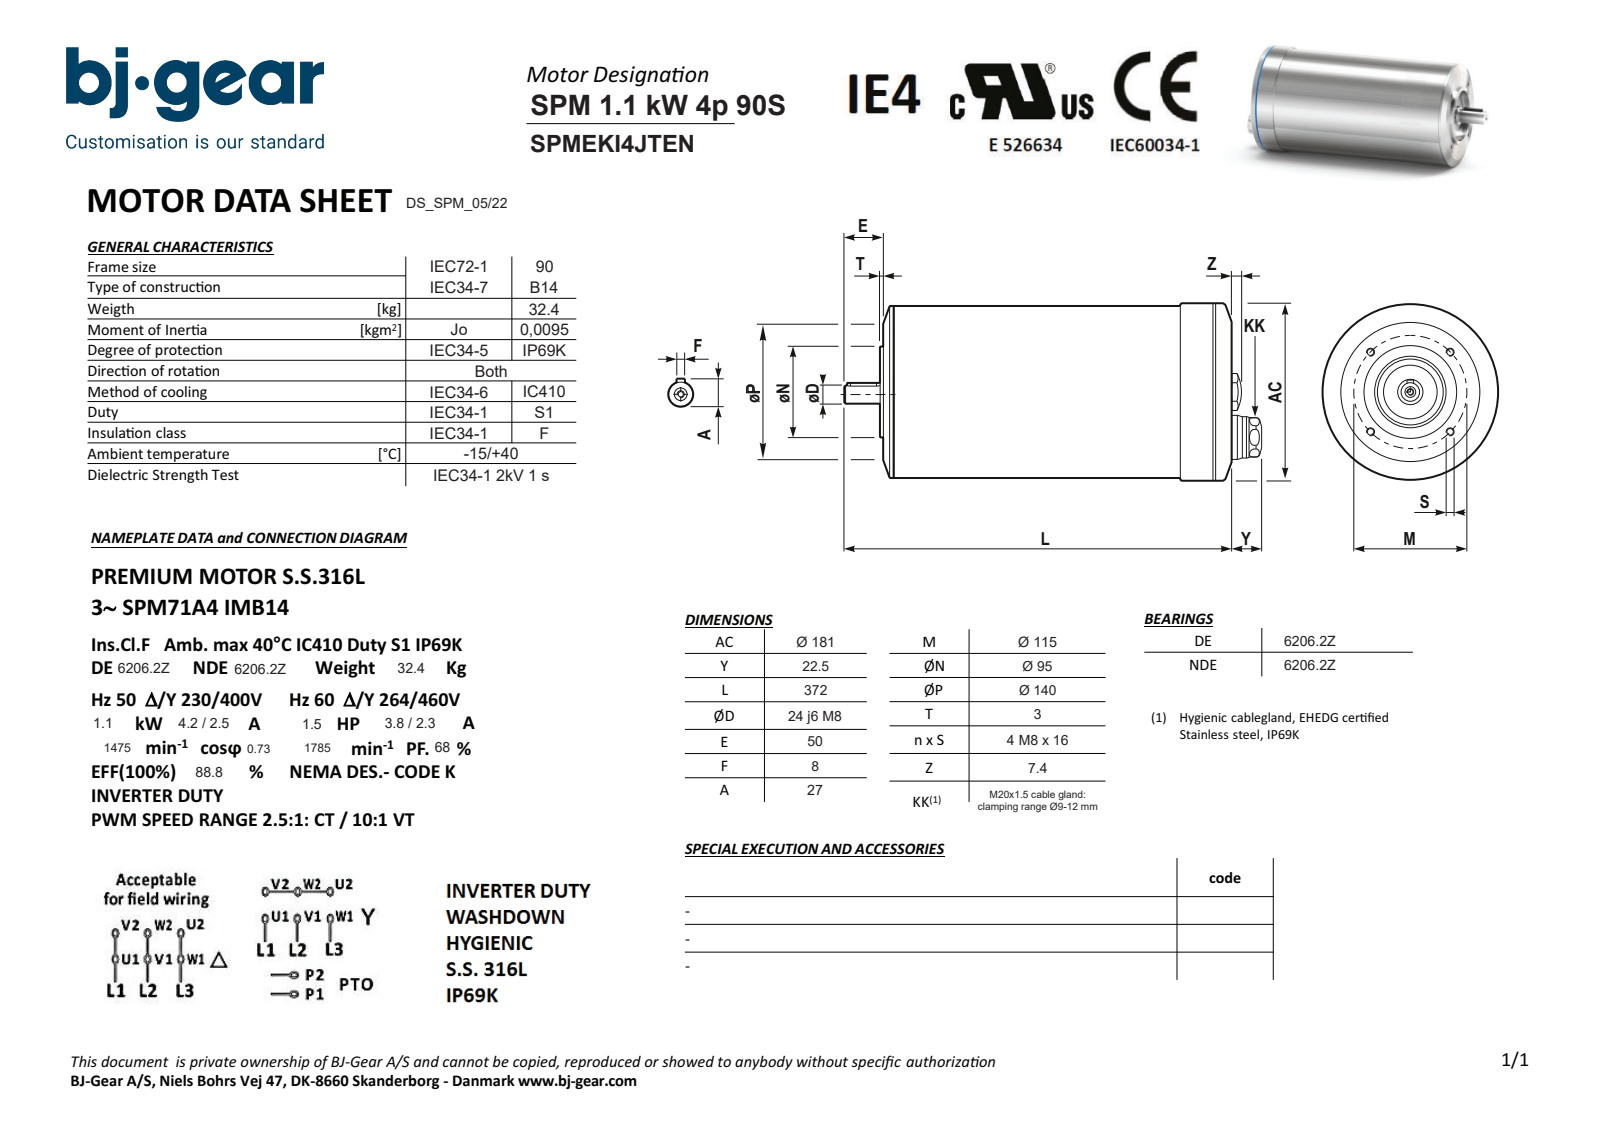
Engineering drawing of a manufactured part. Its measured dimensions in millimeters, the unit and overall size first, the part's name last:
Units: millimetres
Overall size (bounding box): 399.5 × 181 × 181
Round holes (diameter × count): ⌀6.65 ×4, ⌀4.92 ×1, ⌀7 ×1, ⌀8.4 ×1, ⌀13.4 ×1, ⌀85 ×1
Round bosses / shafts (diameter × count): ⌀181 ×1, ⌀180.98 ×1, ⌀178 ×1, ⌀177.98 ×1, ⌀95 ×1, ⌀30 ×1, ⌀24 ×1, ⌀20 ×1
Partial cylindrical surfaces — rounded edges, fillets, slot ends (radius × count): R4 ×2, R12.8 ×1
Main face-to-face distances: 322, 6, 316, 325, 9, 3, 8, 24, 50, 372
Hole centre spacings: 57.5, 81.32, 43.11, 103.94, 115, 55
Volume: 8 014 000 mm³ · Surface area: 238 617 mm²
Bodies: 1 solid, 87 faces (30 planar, 32 cylindrical, 25 other)
Part name (STEP PRODUCT): SPMEKI4JTENN4KSA1-N---NNN
STEP written by: Solid Edge (AUTOMOTIVE_DESIGN)
